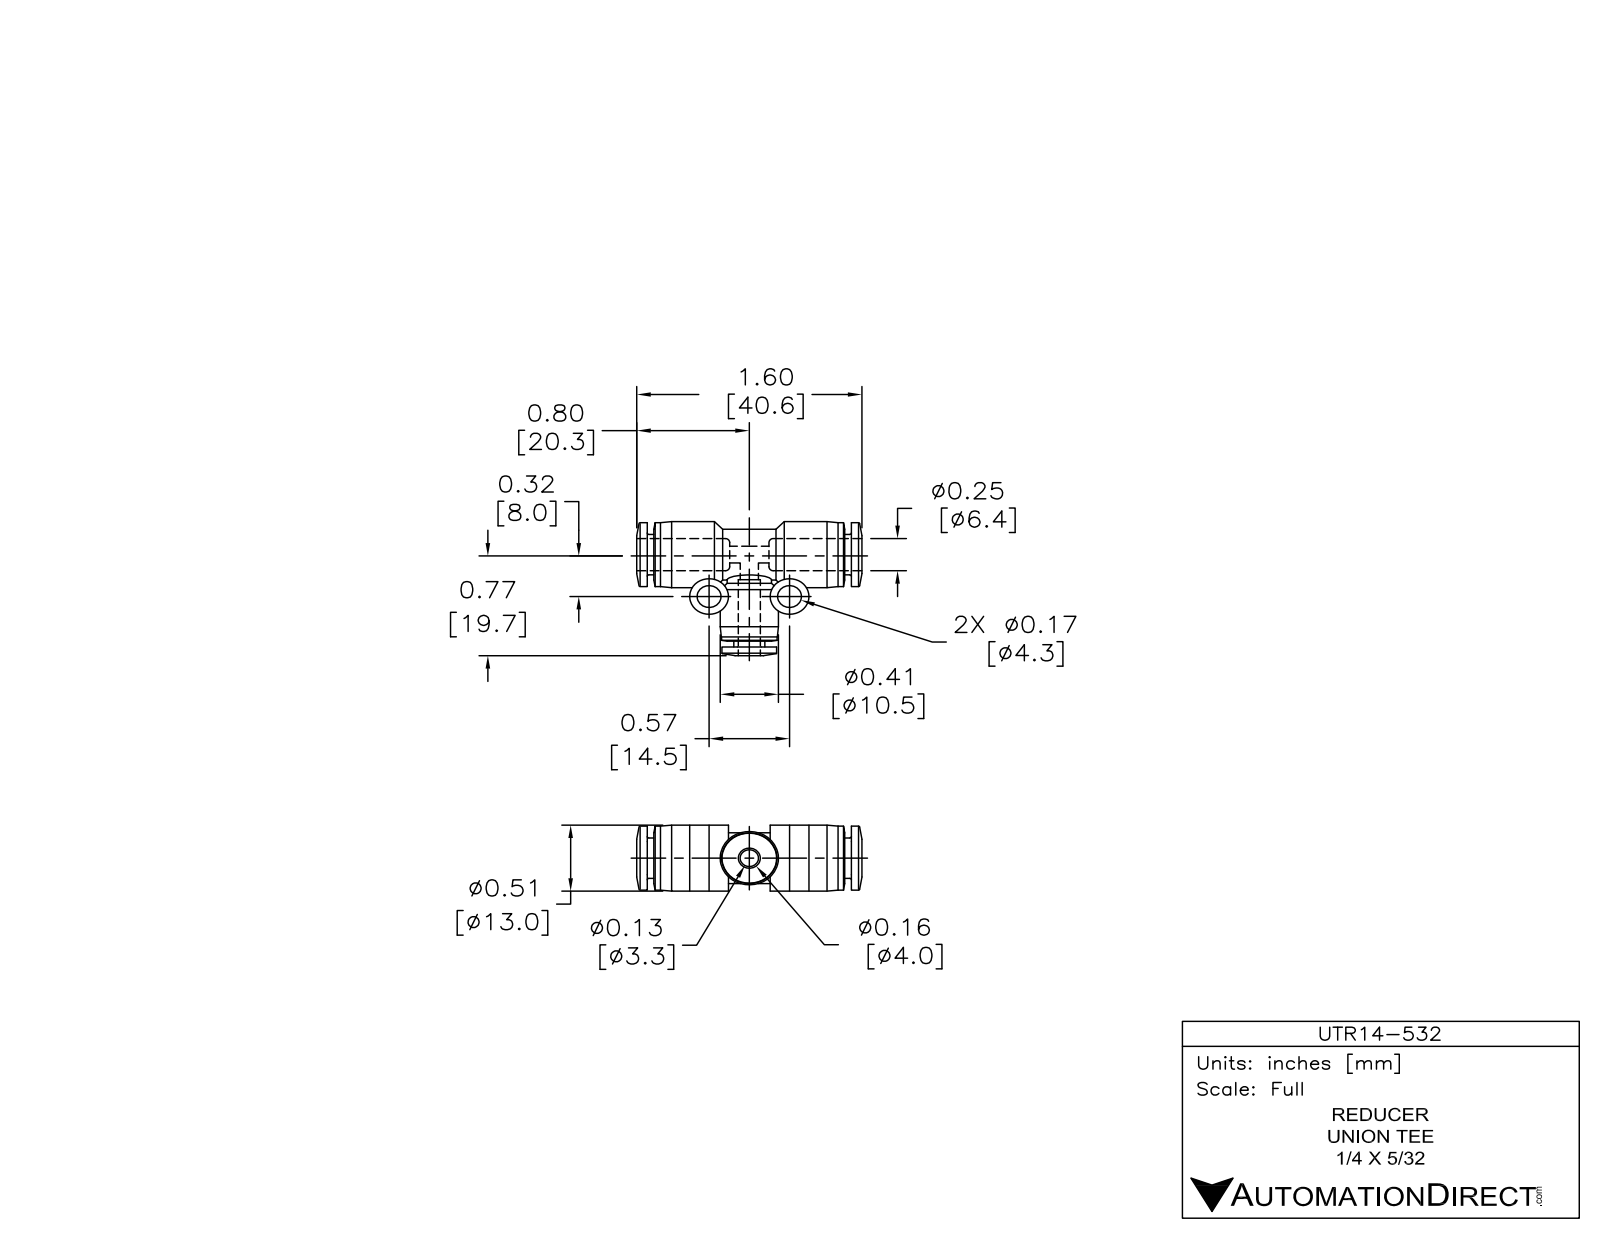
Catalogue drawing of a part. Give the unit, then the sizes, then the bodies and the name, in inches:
Units: inches
Overall size (bounding box): 1.598 × 1.039 × 0.512
Round holes (diameter × count): ⌀0.169 ×3, ⌀0.126 ×2, ⌀0.258 ×1
Round bosses / shafts (diameter × count): ⌀0.394 ×2, ⌀0.276 ×2, ⌀0.512 ×1, ⌀0.496 ×1, ⌀0.413 ×1, ⌀0.388 ×1, ⌀0.315 ×1, ⌀0.313 ×1
Main face-to-face distances: 1.449, 0.047, 1.402, 0.587, 0.862, 0.539, 0.815, 0.512, 1.354, 0.276
Hole centre spacings: 0.571
Volume: 0.286 in³ · Surface area: 6.692 in²
Bodies: 1 solid, 109 faces (15 planar, 46 cylindrical, 48 other)
Part name (STEP PRODUCT): UTR14-532
STEP written by: SolidWorks 2015 (AUTOMOTIVE_DESIGN)
